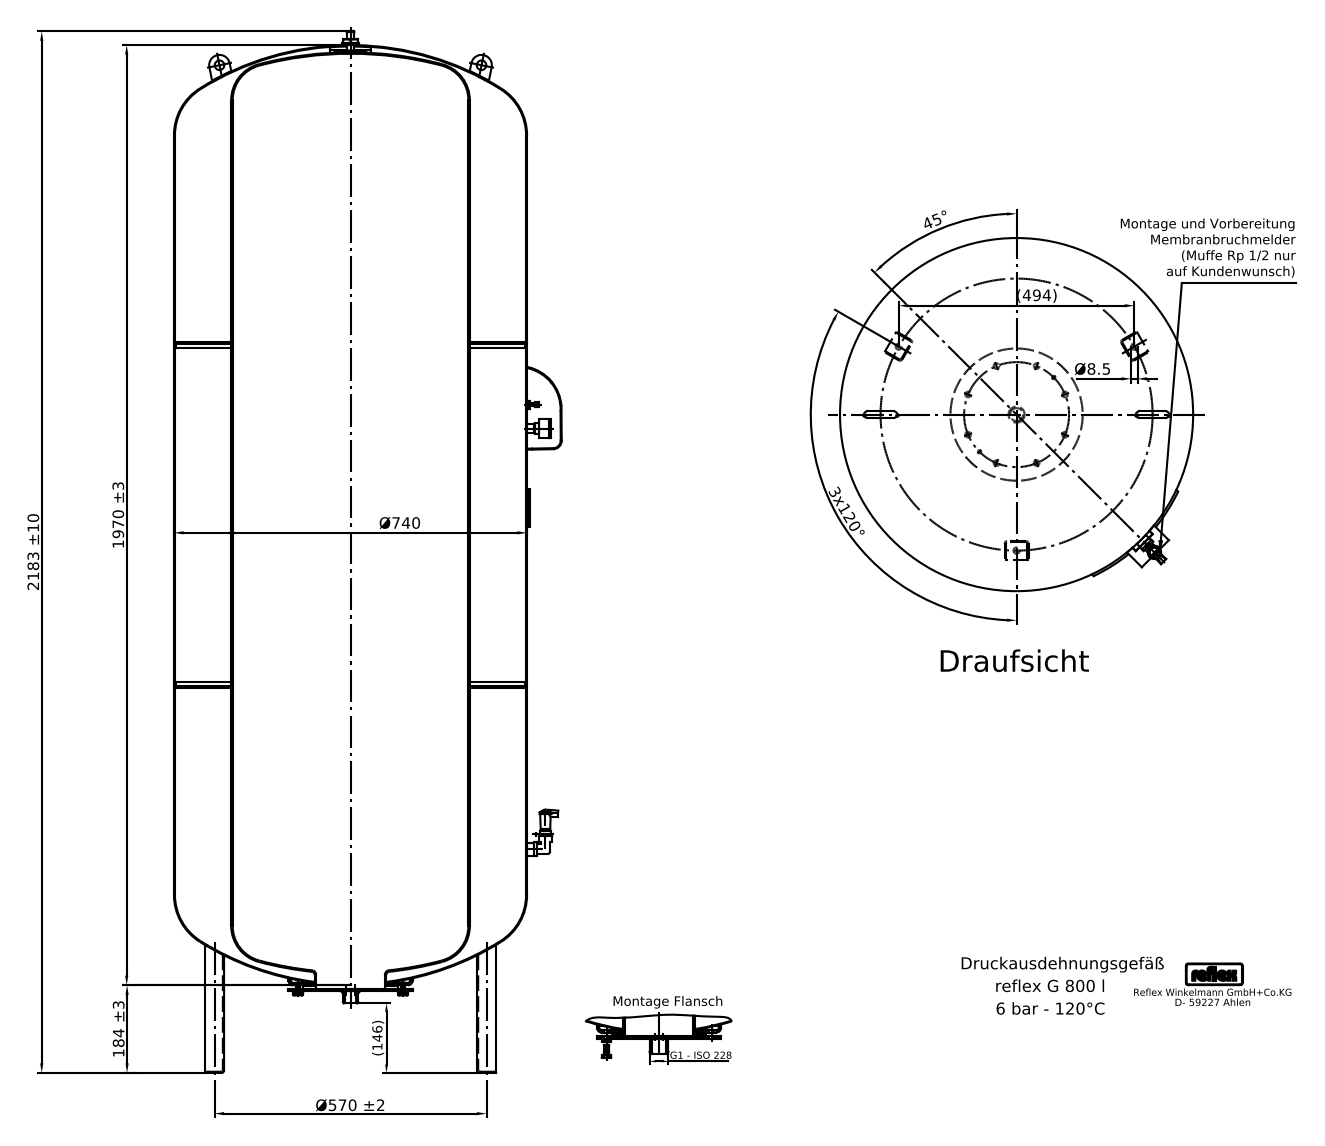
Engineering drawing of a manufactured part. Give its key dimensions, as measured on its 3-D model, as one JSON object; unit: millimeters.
{"step_written_by": "Mechanical Desktop 2008 (CONFIG_CONTROL_DESIGN)", "units": "millimeters", "bodies": {"solids": 22, "faces": 434, "planar": 212, "cylindrical": 138, "other": 84}, "overall_size": [2183, 812, 741.14], "volume_mm3": 793900000, "surface_area_mm2": 7399000, "round_holes": [[10, 1], [161, 1], [250, 1]], "round_bosses_or_shafts": [[10, 9], [20, 3], [28, 2], [26, 2], [24, 2], [740, 1], [260, 1], [230, 1]], "partial_cylinders_radius": [[25, 18], [3.94, 4], [1.57, 3], [9, 3], [2.69, 2], [4.72, 2], [6.49, 2], [6.58, 2]], "face_to_face_distances": [1592, 6, 196, 1788, 202, 1794, 171, 5, 5.88, 17.75], "hole_center_spacings": [385.5]}
